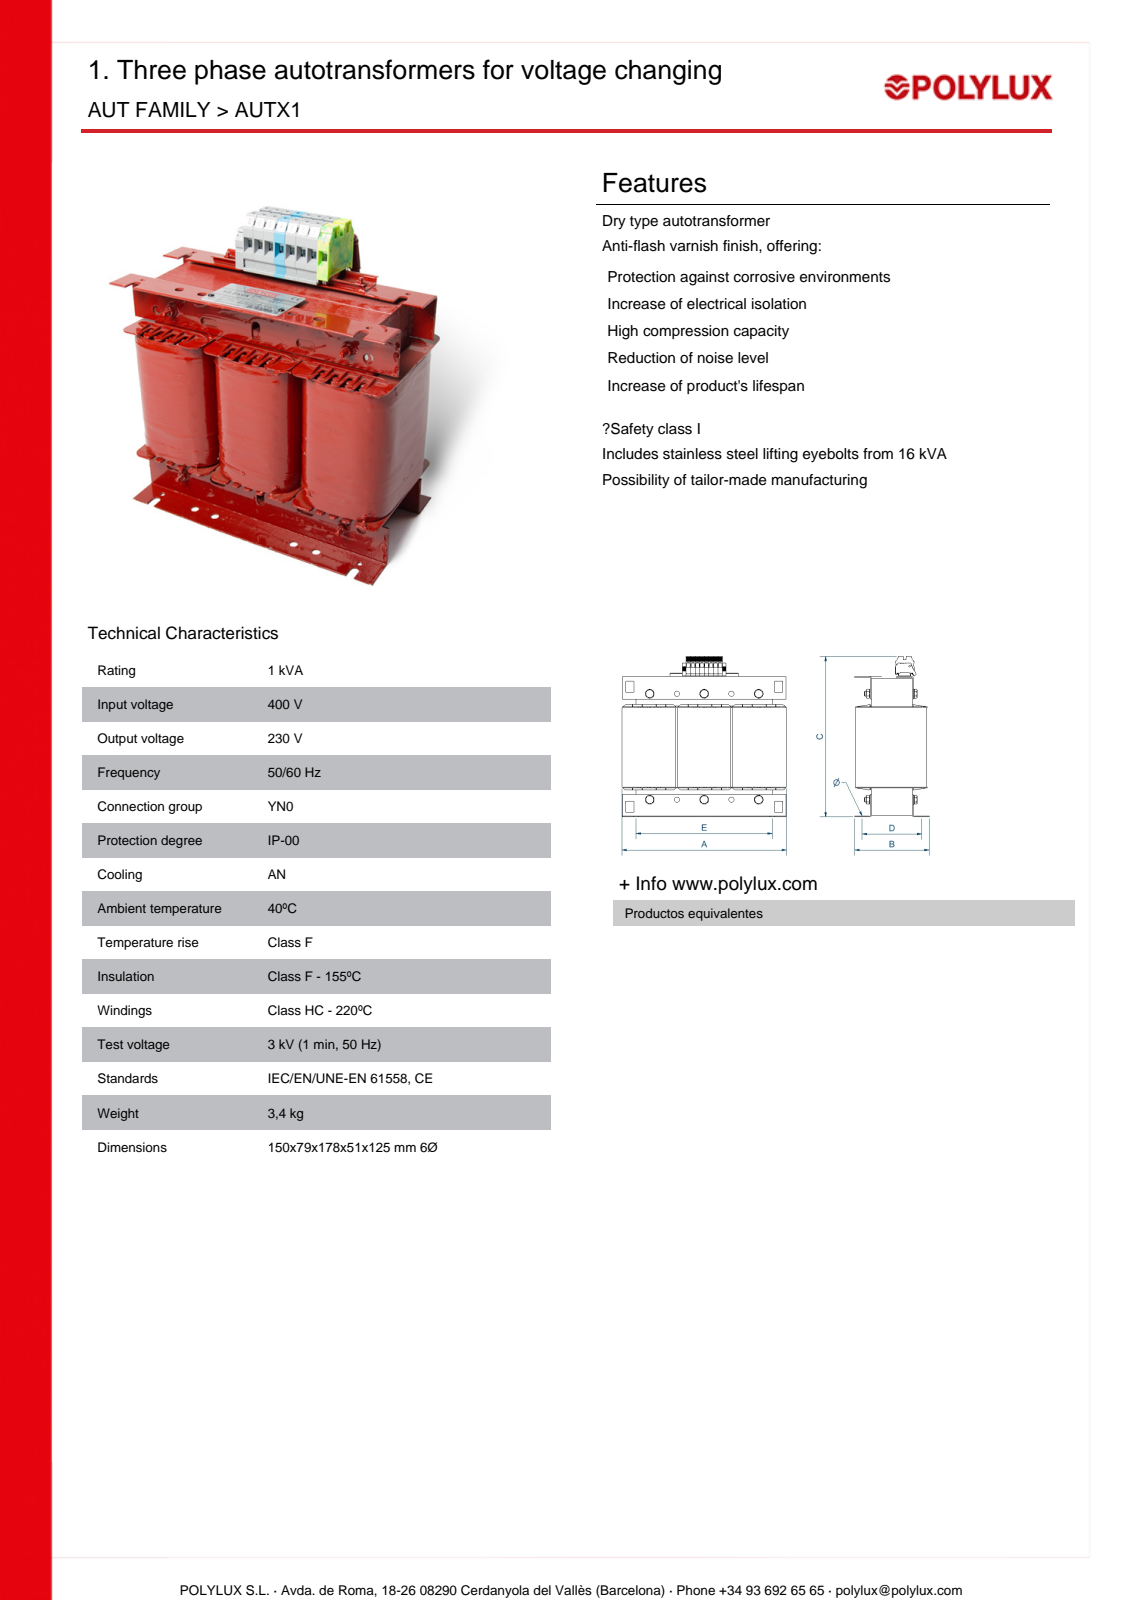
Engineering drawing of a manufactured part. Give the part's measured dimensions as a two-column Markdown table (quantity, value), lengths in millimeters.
| quantity | value |
| --- | --- |
| part name | AUTX1; Núcleo 25x25 EI III; Subensamble carrete y bobina 25x25; Carrete 25x25 EI III (+8 more) |
| STEP written by | Autodesk Inventor 2018 (AUTOMOTIVE_DESIGN) |
| units | millimeters |
| bodies | 36 solids, 1819 faces (1154 planar, 621 cylindrical, 44 other) |
| overall size | 183.15 × 150 × 82.5 |
| volume | 968 516 mm³ |
| surface area | 325 423 mm² |
| round holes (diameter × count) | 4.3 × 16, 4.92 × 8, 3.5 × 6, 7 × 6, 6 × 4, 6.4 × 4 |
| round bosses / shafts (diameter × count) | 12 × 4, 8.9 × 4 |
| partial cylindrical surfaces (radius × count) | 3 × 36, 2 × 16, 24.01 × 16, 10 × 14, 0.1 × 12, 6 × 12, 0.3 × 11, 1 × 10 |
| main face-to-face distances | 2, 27, 50, 30, 25, 29, 1, 33, 20, 47 |
| hole center spacings | 6, 16.71, 12, 19.68, 18, 23.82, 15.6, 24 |
